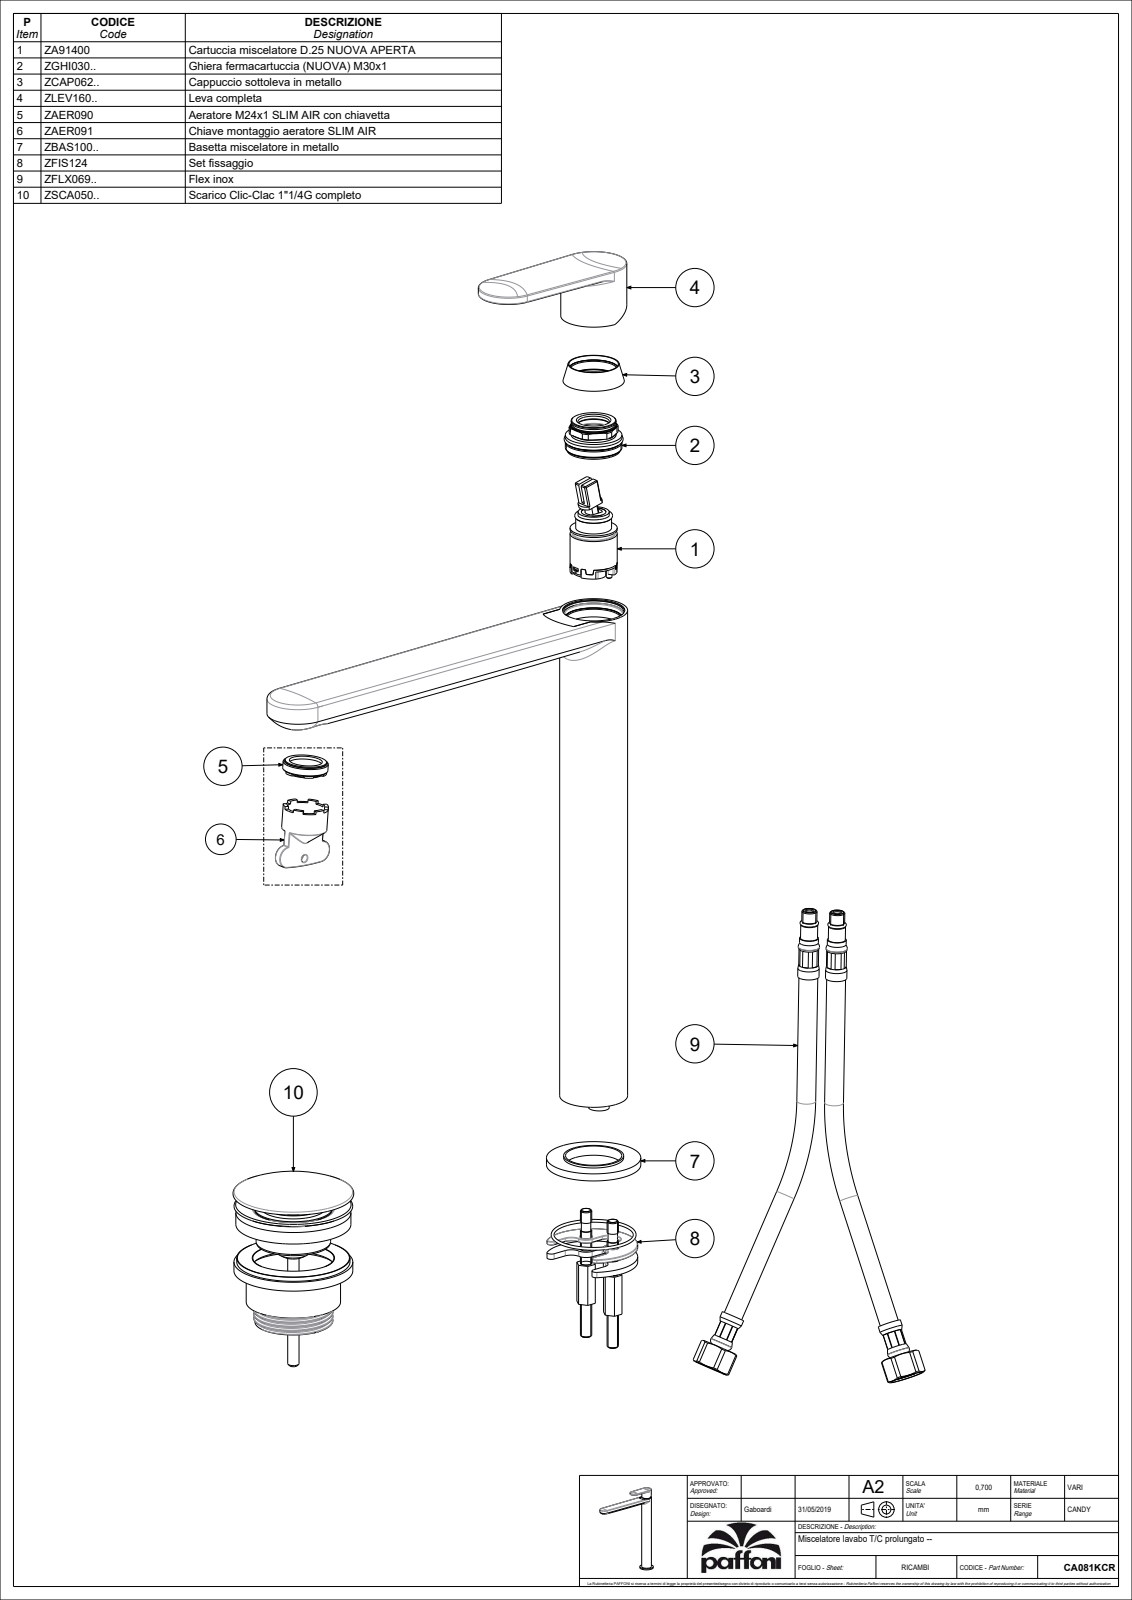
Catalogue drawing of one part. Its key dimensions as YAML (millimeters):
part_name: "CA081CR"
step_written_by: "CREO PARAMETRIC BY PTC INC, 2020044 (CONFIG_CONTROL_DESIGN)"
units: millimeters
bodies: {solids: 2, faces: 182, planar: 61, cylindrical: 58, other: 63}
overall_size: [310.12, 246, 50]
volume: 421950
surface_area: 69619
round_holes:
  - {diameter: 3, count: 1}
  - {diameter: 4.5, count: 1}
  - {diameter: 24.5, count: 1}
  - {diameter: 24.8, count: 1}
  - {diameter: 26.2, count: 1}
  - {diameter: 28, count: 1}
round_bosses_or_shafts:
  - {diameter: 50, count: 1}
  - {diameter: 36, count: 1}
  - {diameter: 35, count: 1}
  - {diameter: 24, count: 1}
  - {diameter: 18.5, count: 1}
  - {diameter: 7.6, count: 1}
  - {diameter: 5.5, count: 1}
partial_cylinders:
  - {radius: 3, count: 4}
  - {radius: 3.5, count: 1}
  - {radius: 9.75, count: 1}
  - {radius: 11.5, count: 1}
  - {radius: 16, count: 1}
  - {radius: 16.5, count: 1}
  - {radius: 27.5, count: 1}
face_to_face_distances: [278, 4, 274, 307.12, 303.12, 29.12, 11.5, 2.5, 14, 9]
